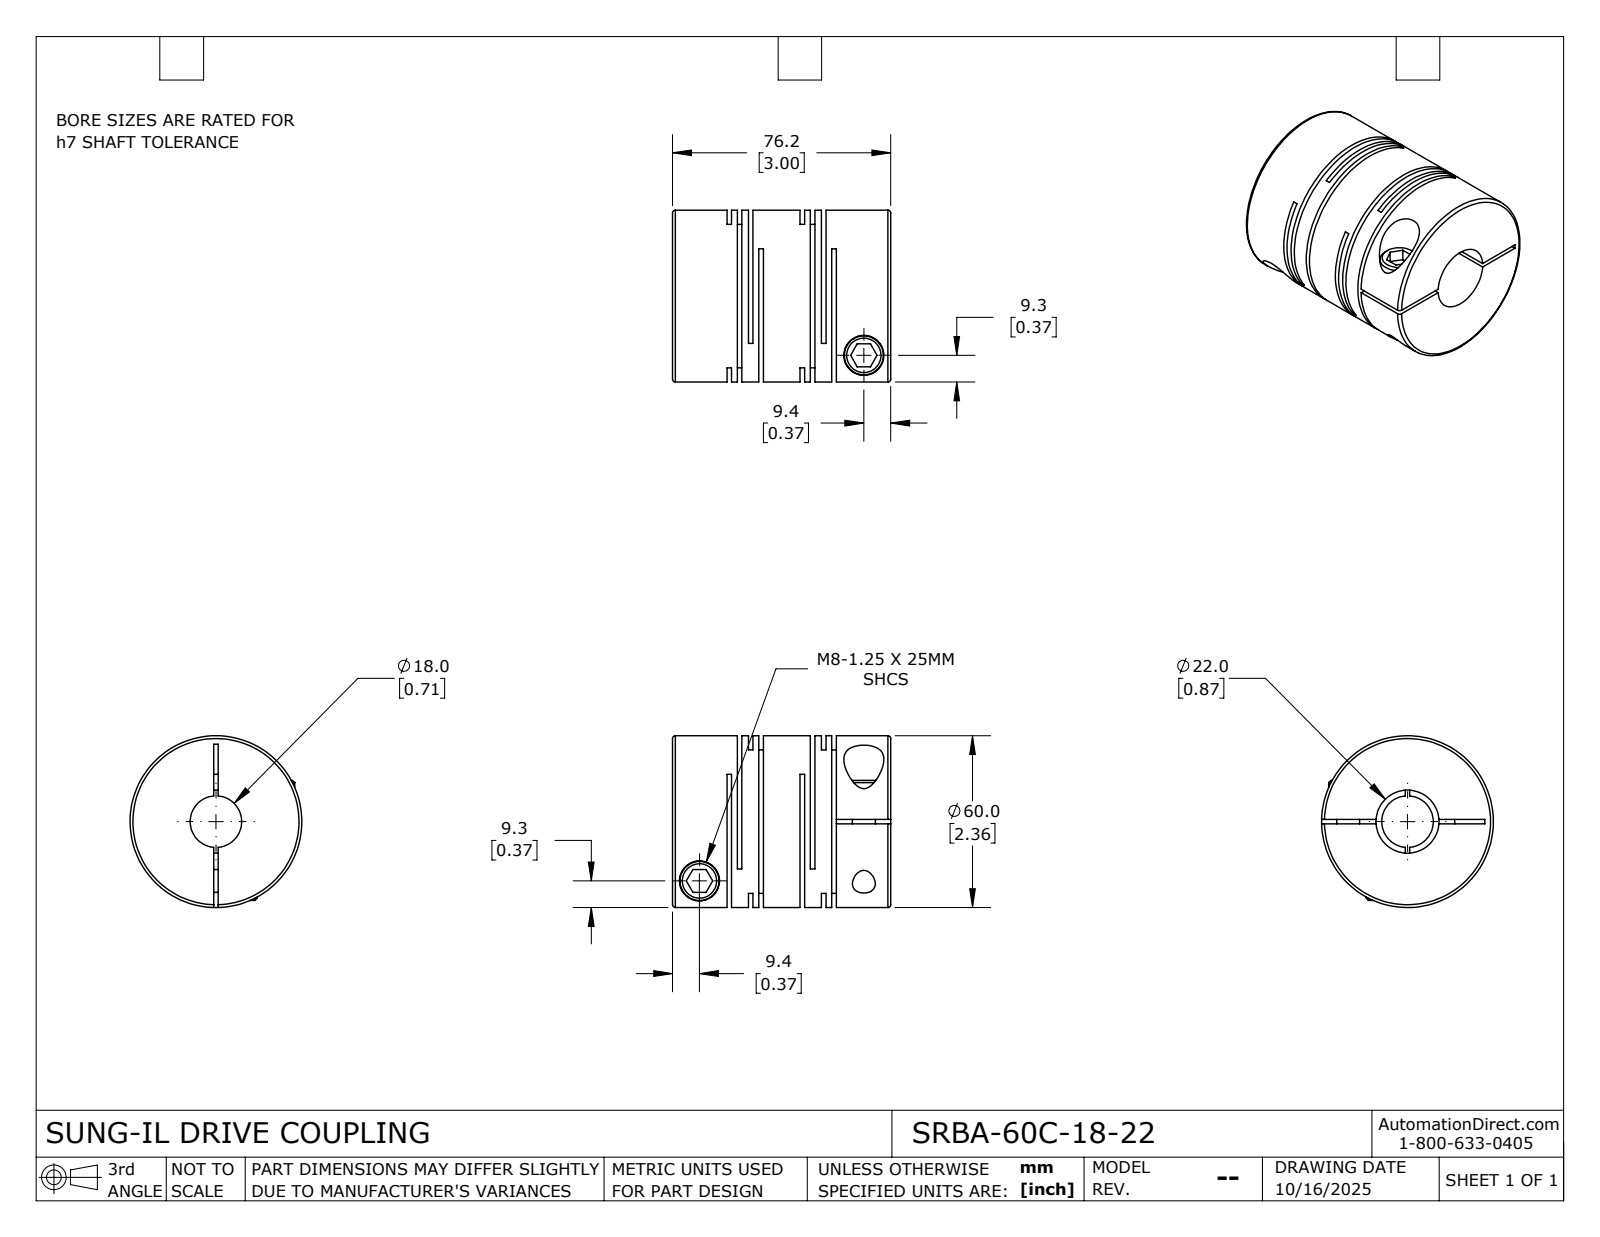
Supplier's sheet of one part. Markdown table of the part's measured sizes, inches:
| quantity | value |
| --- | --- |
| part name | SRBA-60C-18-22 |
| STEP written by | SolidWorks 2024 (CONFIG_CONTROL_DESIGN) |
| units | inches |
| bodies | 1 solid, 115 faces (60 planar, 42 cylindrical, 13 other) |
| overall size | 3 × 2.362 × 2.362 |
| volume | 9.671 in³ |
| surface area | 90.43 in² |
| round holes (diameter × count) | 0.315 × 2, 0.551 × 2, 0.709 × 1, 0.866 × 1 |
| round bosses / shafts (diameter × count) | 0.535 × 2, 2.362 × 1 |
| main face-to-face distances | 0.063, 0.142, 0.295, 1.004, 1.299, 0.079, 0.232, 0.154, 0.941, 0.862 |
